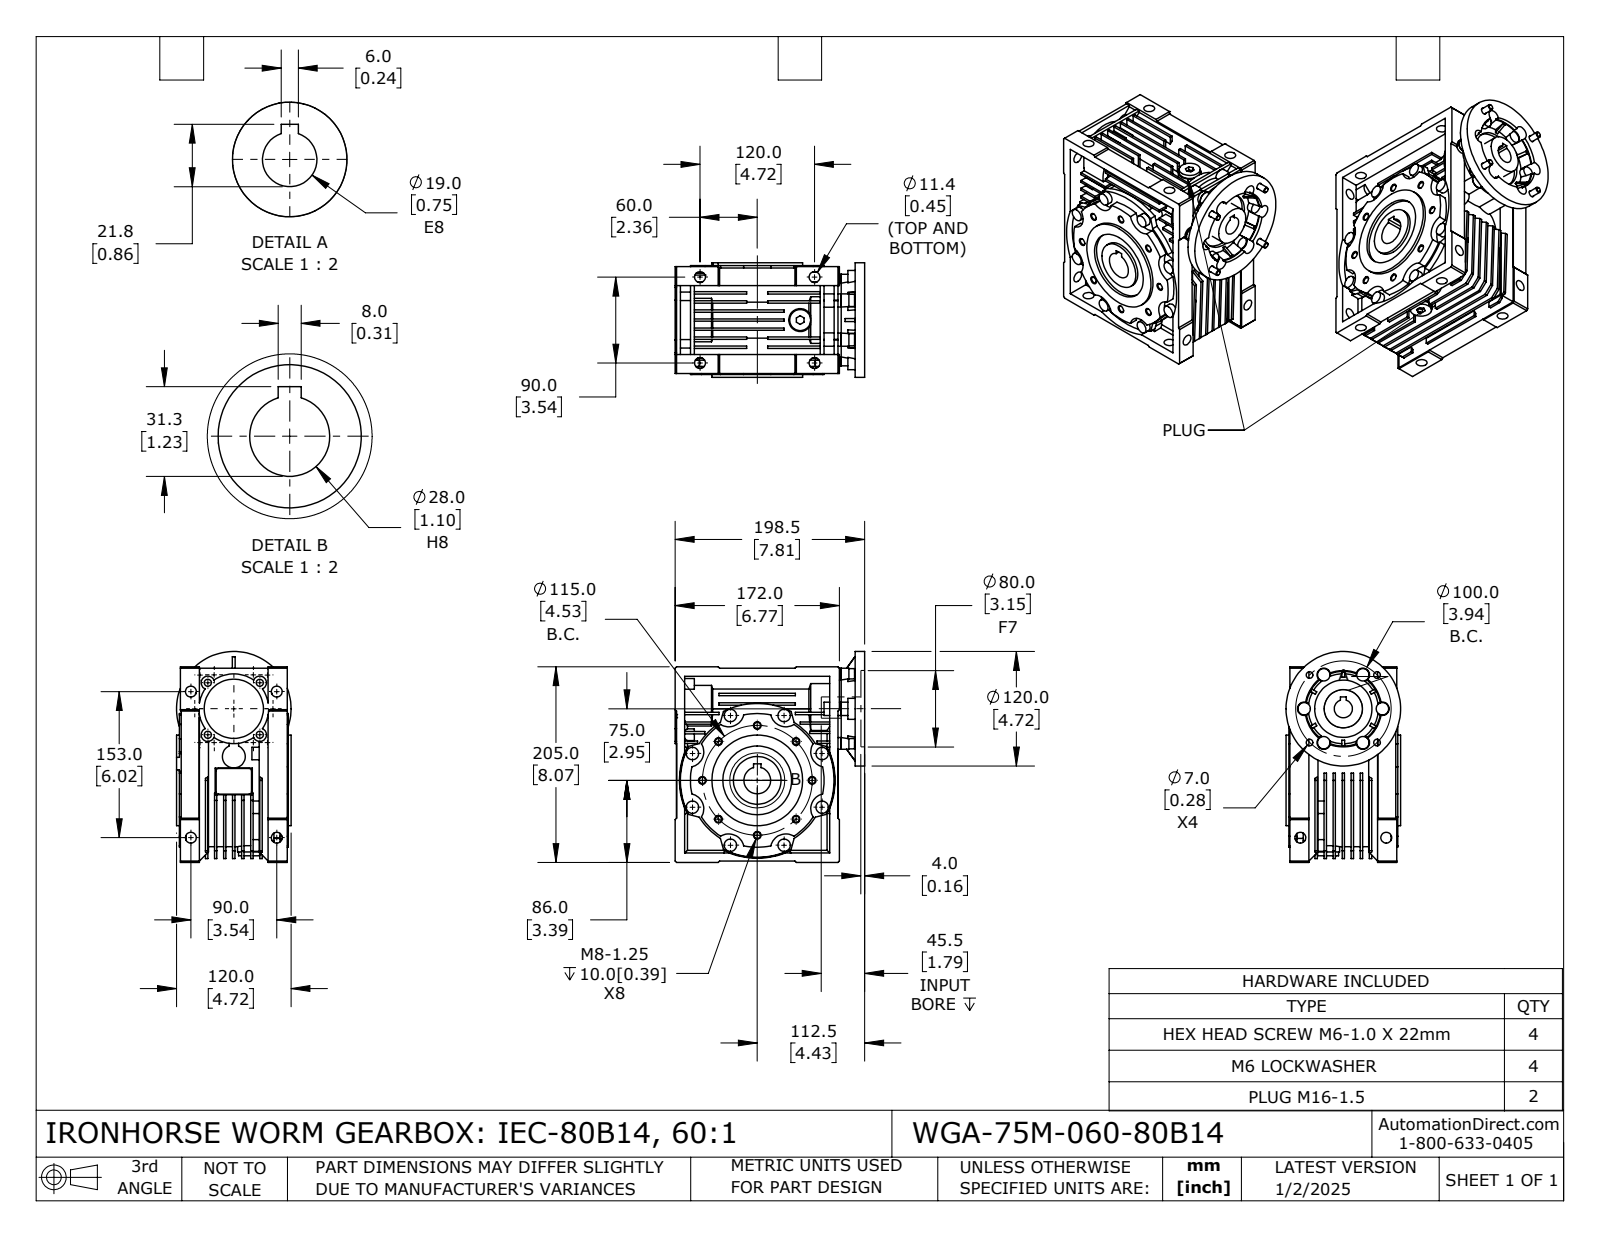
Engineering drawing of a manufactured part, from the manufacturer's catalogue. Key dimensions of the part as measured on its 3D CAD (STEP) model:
Part name (STEP PRODUCT): WGA-75M-060-80B14
STEP written by: SolidWorks 2024 (CONFIG_CONTROL_DESIGN)
Units: millimetres
Bodies: 16 solids, 1304 faces (703 planar, 433 cylindrical, 168 other)
Overall size (bounding box): 221 × 209 × 120
Volume: 2 853 000 mm³ · Surface area: 480 911 mm²
Round holes (diameter × count): ⌀6.65 ×8, ⌀11.38 ×8, ⌀6.1 ×4, ⌀7 ×4, ⌀7.45 ×4, ⌀14.5 ×2, ⌀19 ×1, ⌀20 ×1, ⌀28 ×1, ⌀39 ×1, ⌀42 ×1, ⌀50 ×1
Round bosses / shafts (diameter × count): ⌀13 ×14, ⌀12.2 ×4, ⌀6 ×4, ⌀24 ×3, ⌀22 ×2, ⌀15.8 ×2, ⌀13.7 ×2, ⌀139.93 ×1
Partial cylindrical surfaces — rounded edges, fillets, slot ends (radius × count): R7 ×10, R16 ×8, R11 ×6, R2.5 ×4, R36 ×1, R36.5 ×1, R39 ×1, R40 ×1
Main face-to-face distances: 9.5, 2.5, 19, 12, 10, 7, 16.5, 28.5, 27.75, 21.5
Hole centre spacings: 44.01, 57.5, 63.11, 81.32, 106.25, 11.51, 38.49, 50.01
